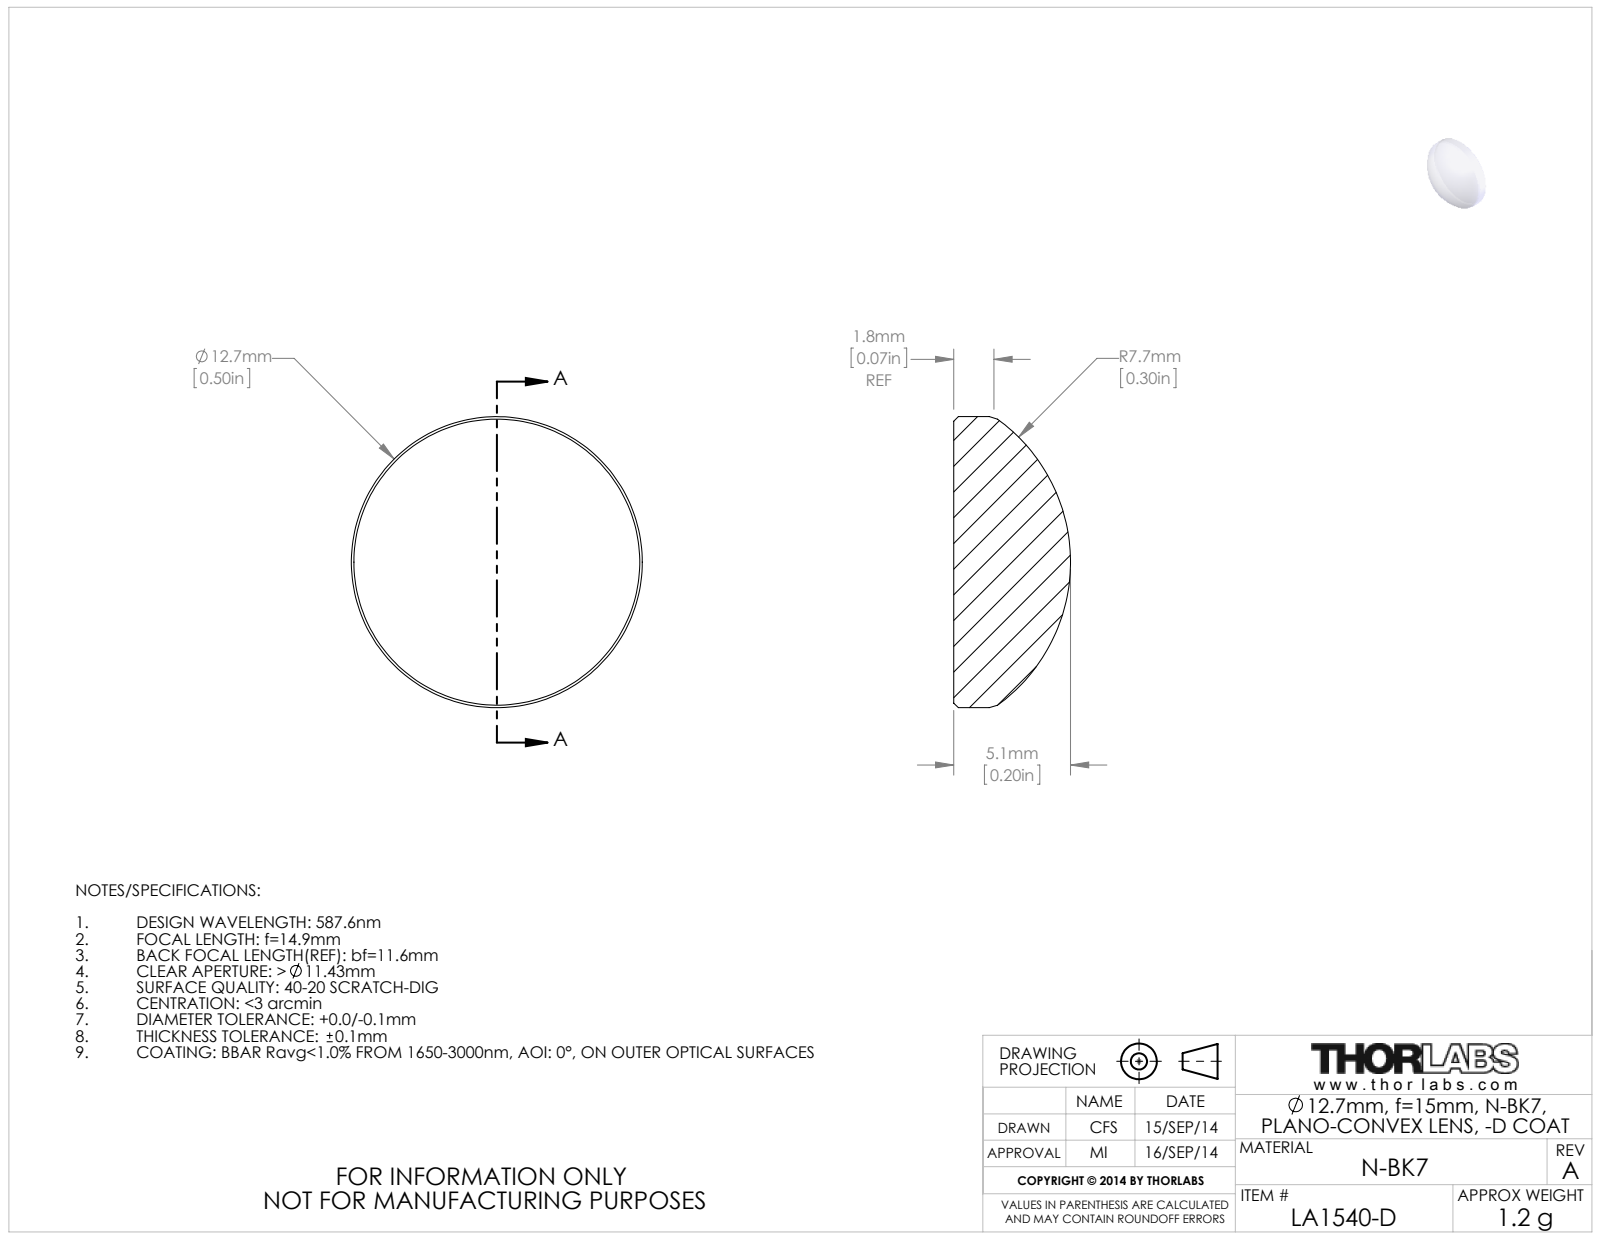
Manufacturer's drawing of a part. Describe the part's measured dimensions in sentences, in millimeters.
The part is named "TTN031781-E0W". Its 3-D file was written by "SolidWorks 2014 (CONFIG_CONTROL_DESIGN)". It is 1 solid with 9 faces: 1 planar, 2 cylindrical and 6 other. Overall it measures 12.7 by 12.7 by 5.1 millimeters. Its volume is 460 cubic millimeters and its surface area 353 square millimeters. Round bosses or shafts: 1 of diameter 12.7.
